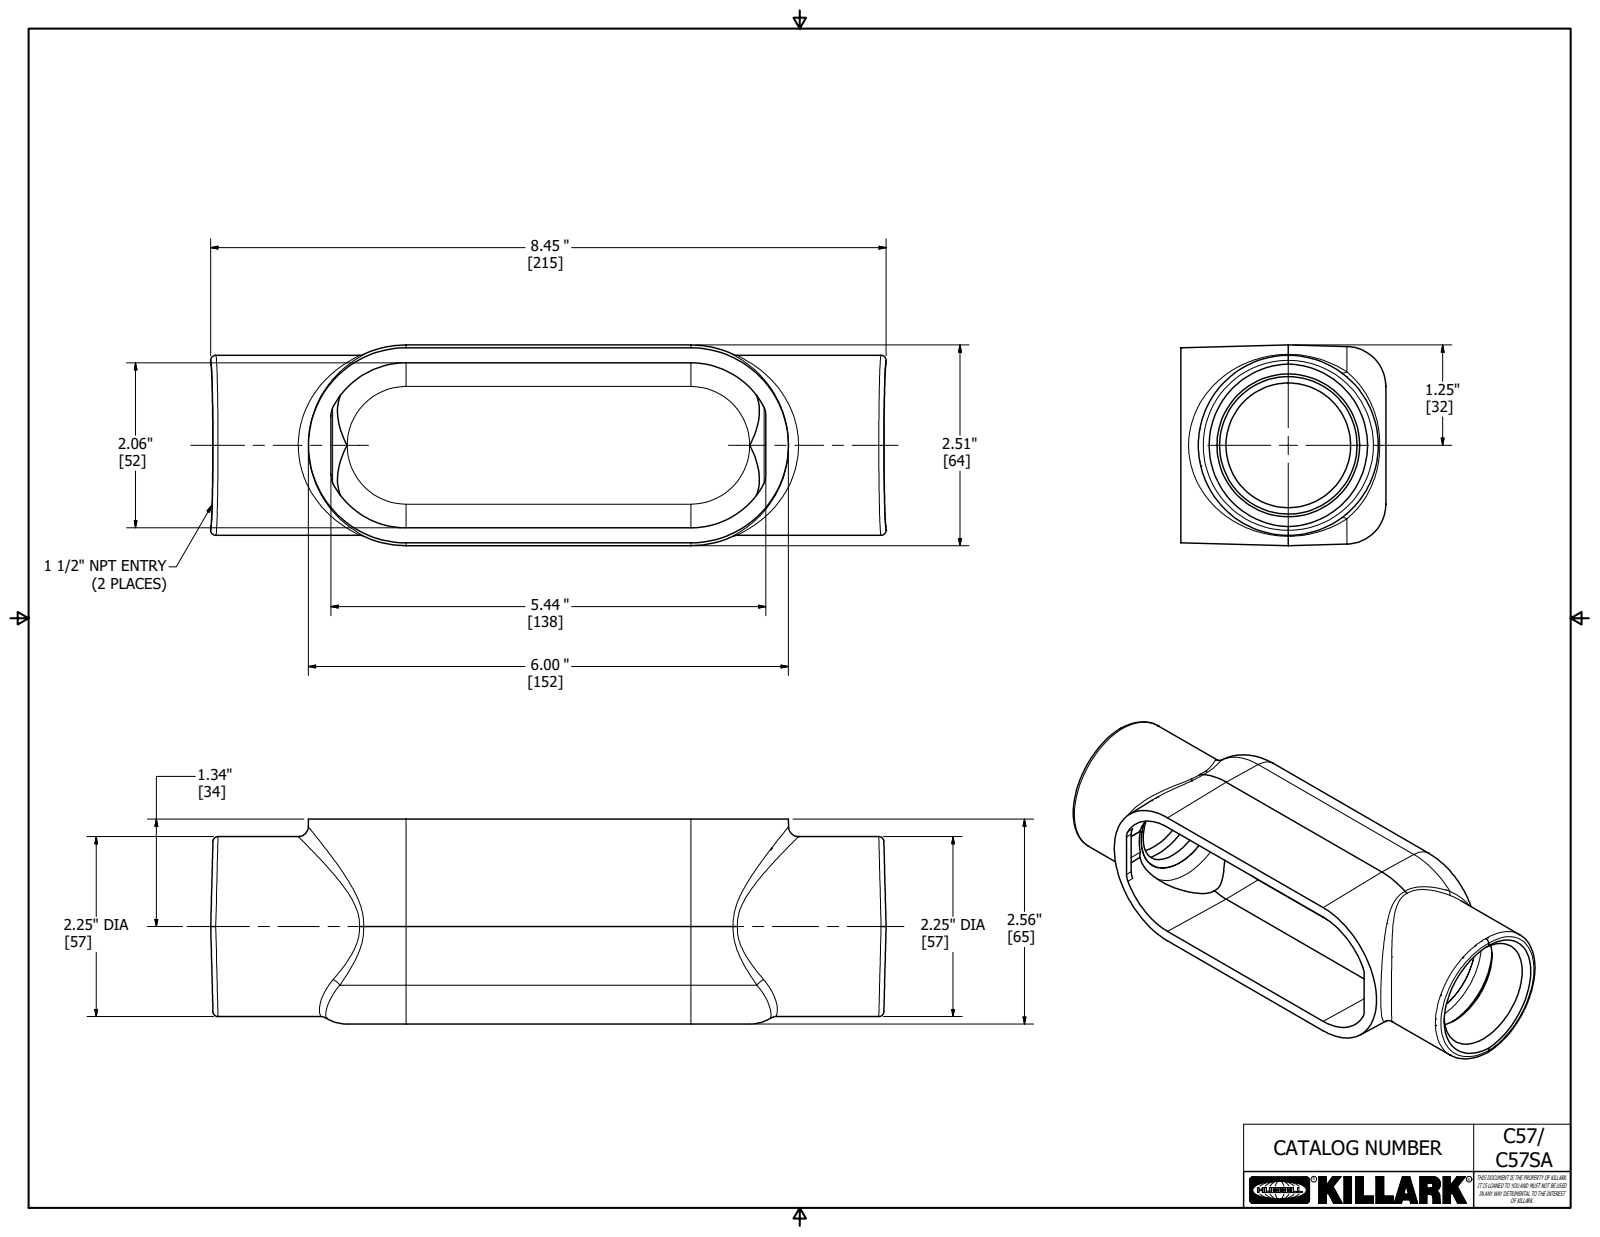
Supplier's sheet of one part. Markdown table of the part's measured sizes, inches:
| quantity | value |
| --- | --- |
| part name | 17694 |
| STEP written by | Autodesk Inventor 2018 (AUTOMOTIVE_DESIGN) |
| units | inches |
| bodies | 1 solid, 96 faces (30 planar, 18 cylindrical, 48 other) |
| overall size | 8.445 × 2.562 × 2.508 |
| volume | 11.2 in³ |
| surface area | 122.3 in² |
| round holes (diameter × count) | 1.906 × 1, 2.063 × 1 |
| round bosses / shafts (diameter × count) | 2.25 × 1 |
| partial cylindrical surfaces (radius × count) | 0.05 × 4, 0.125 × 4, 0.313 × 2, 0.5 × 2 |
| main face-to-face distances | 0.188, 2.321, 0.187, 2.509, 2.133, 2.562, 2.374, 0.031, 0.156, 2.531 |
